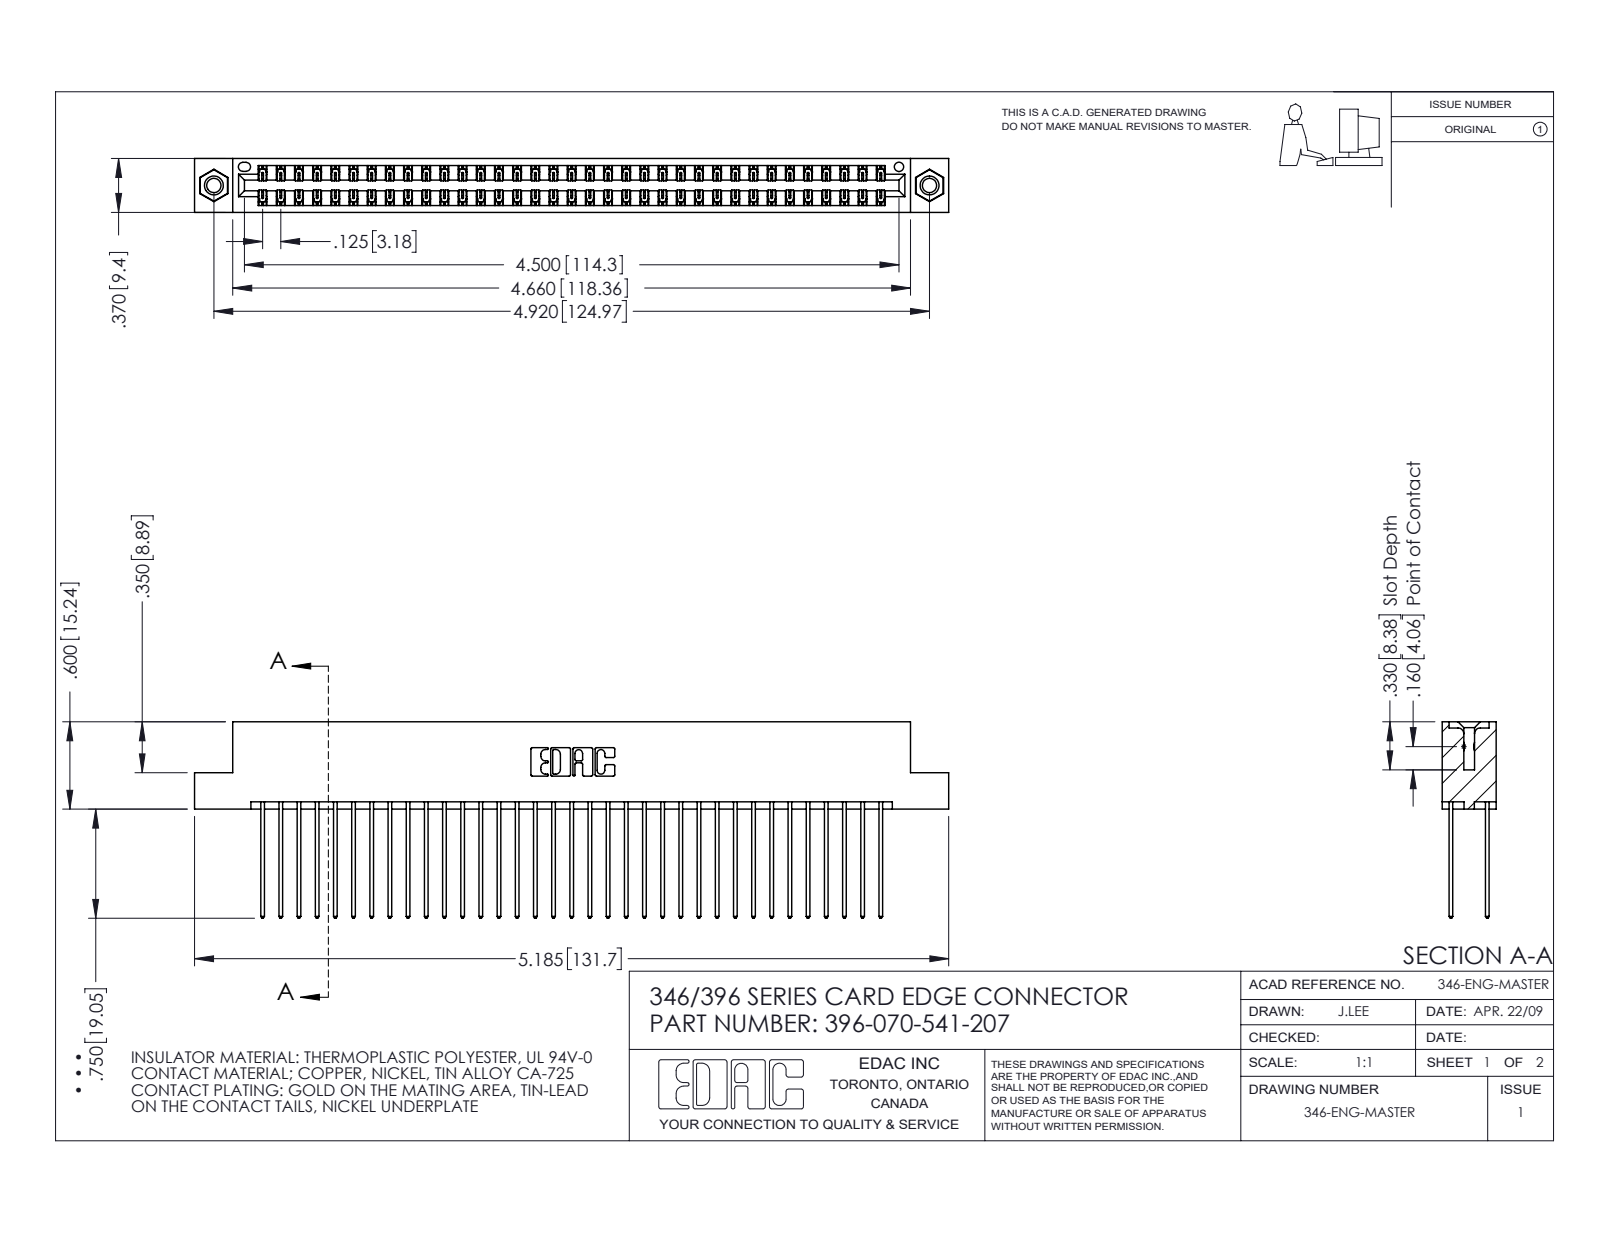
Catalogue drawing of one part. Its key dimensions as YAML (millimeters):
part_name: "345-250-001_345-250-005-103; 346 Part_Flush Mounting Lugs - 0.156 Dia-TI; 345-292-001_345-293-141; 396-070-541-207"
step_written_by: "SolidWorks 2016 (CONFIG_CONTROL_DESIGN)"
units: millimeters
bodies: {solids: 73, faces: 3822, planar: 2558, cylindrical: 1248, other: 16}
overall_size: [131.7, 34.3, 9.4]
volume: 13200
surface_area: 19960
round_holes:
  - {diameter: 2.5, count: 2}
  - {diameter: 3.2, count: 2}
  - {diameter: 4, count: 2}
  - {diameter: 1.6, count: 1}
round_bosses_or_shafts:
  - {diameter: 3.9, count: 2}
partial_cylinders:
  - {radius: 0.2, count: 105}
  - {radius: 0.3, count: 70}
  - {radius: 0.3, count: 22}
  - {radius: 0.2, count: 6}
  - {radius: 0.8, count: 6}
  - {radius: 0.7, count: 3}
  - {radius: 0.4, count: 2}
  - {radius: 0.6, count: 2}
face_to_face_distances: [1.2, 8.2, 6.4, 1.8, 7.6, 0.6, 9.4, 7, 5.7, 3.8]
hole_center_spacings: [6.2, 119.7, 125]
